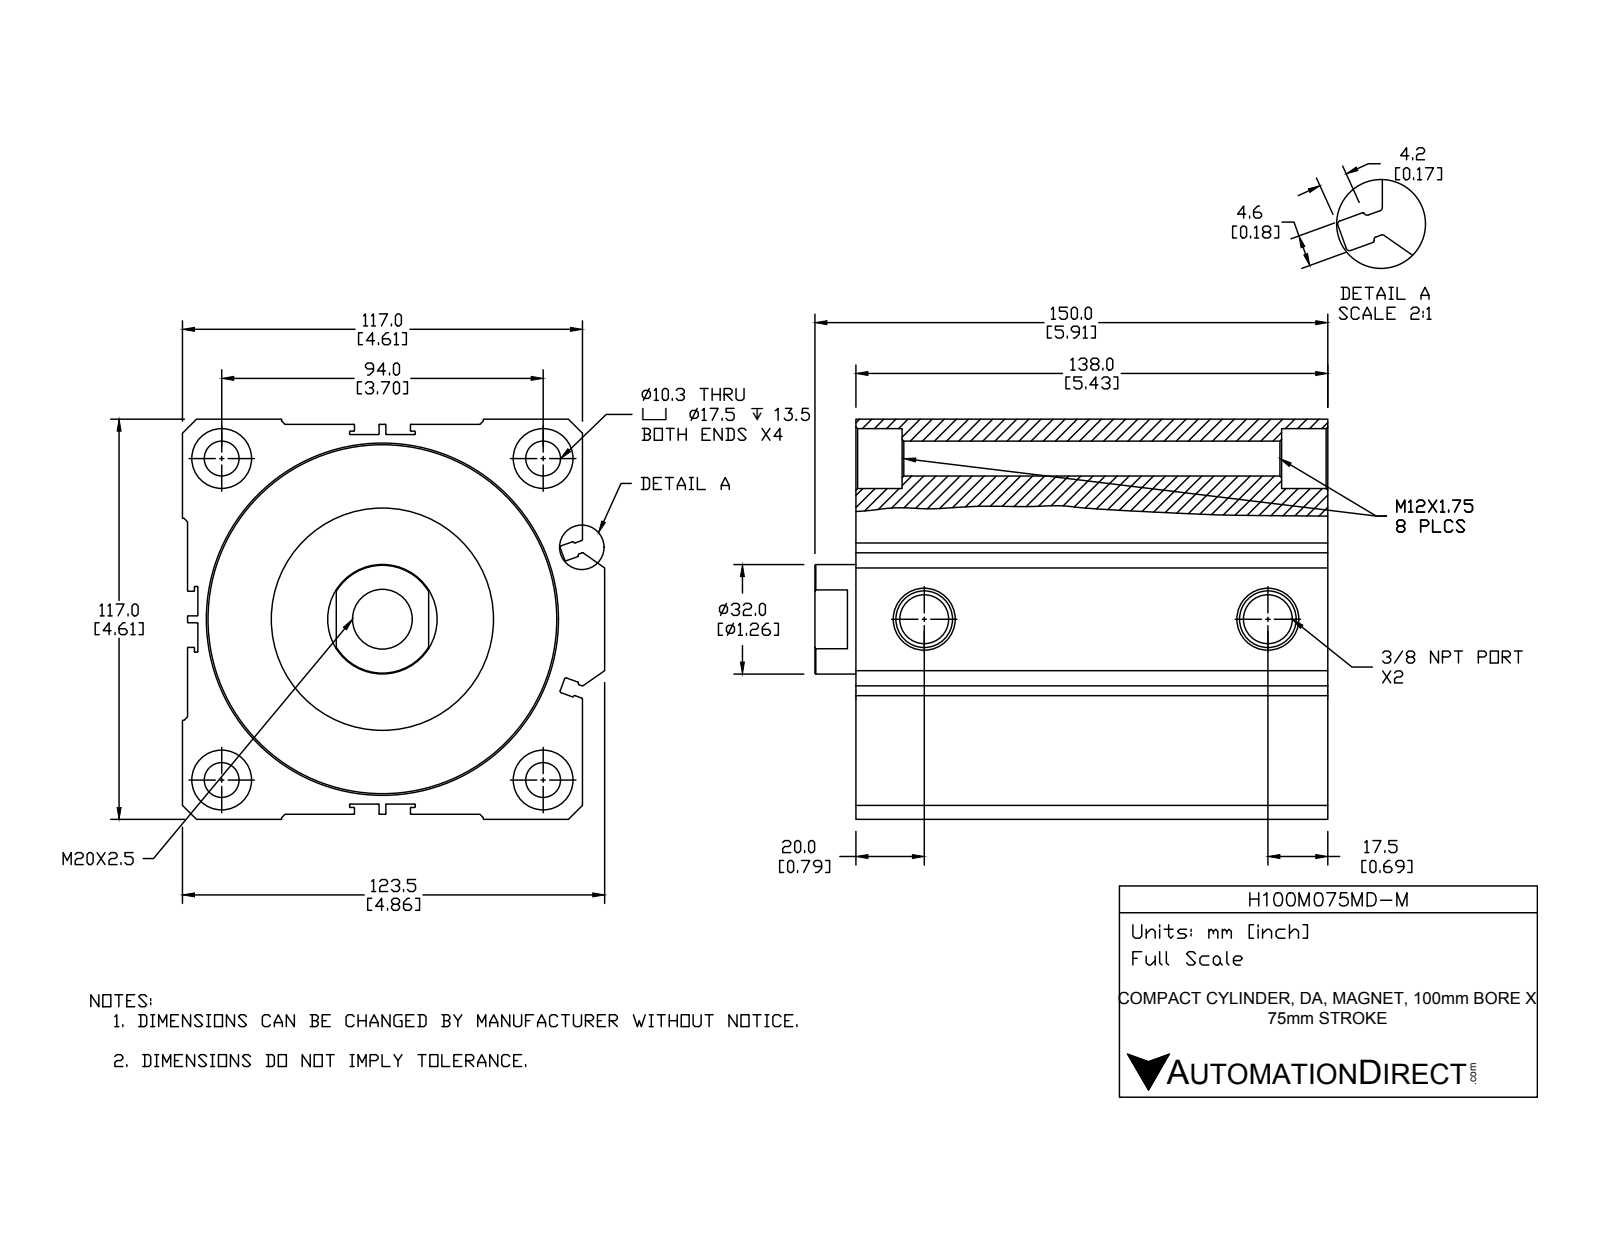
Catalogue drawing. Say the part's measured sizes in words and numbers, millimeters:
The part is named "H100M075MD-M; H100M075MD-M-PISTON; H100M075MD-M-BODY". Its 3-D file was written by "SolidWorks 2015 (CONFIG_CONTROL_DESIGN)". It is 2 solids with 261 faces: 105 planar, 103 cylindrical and 53 other. Overall it measures 150 by 123.5 by 117 millimeters. Its volume is 1 190 000 cubic millimeters and its surface area 214 113 square millimeters. Round holes: 5 of diameter 17.5, 4 of diameter 10.2, 2 of diameter 14.27, 1 of diameter 32, 1 of diameter 65, 1 of diameter 100, 1 of diameter 102. Round bosses or shafts: 1 of diameter 39. Partial cylindrical surfaces (rounded edges, fillets, slot ends): 40 of radius 0.2, 12 of radius 0.5. The main face-to-face distances are 115.5, 1.5, 117, 123.5, 27.8, 103.5, 75.7, 112.5, 4.5, 3. The hole center spacings are 66.47, 94, 132.94, 100.5.
